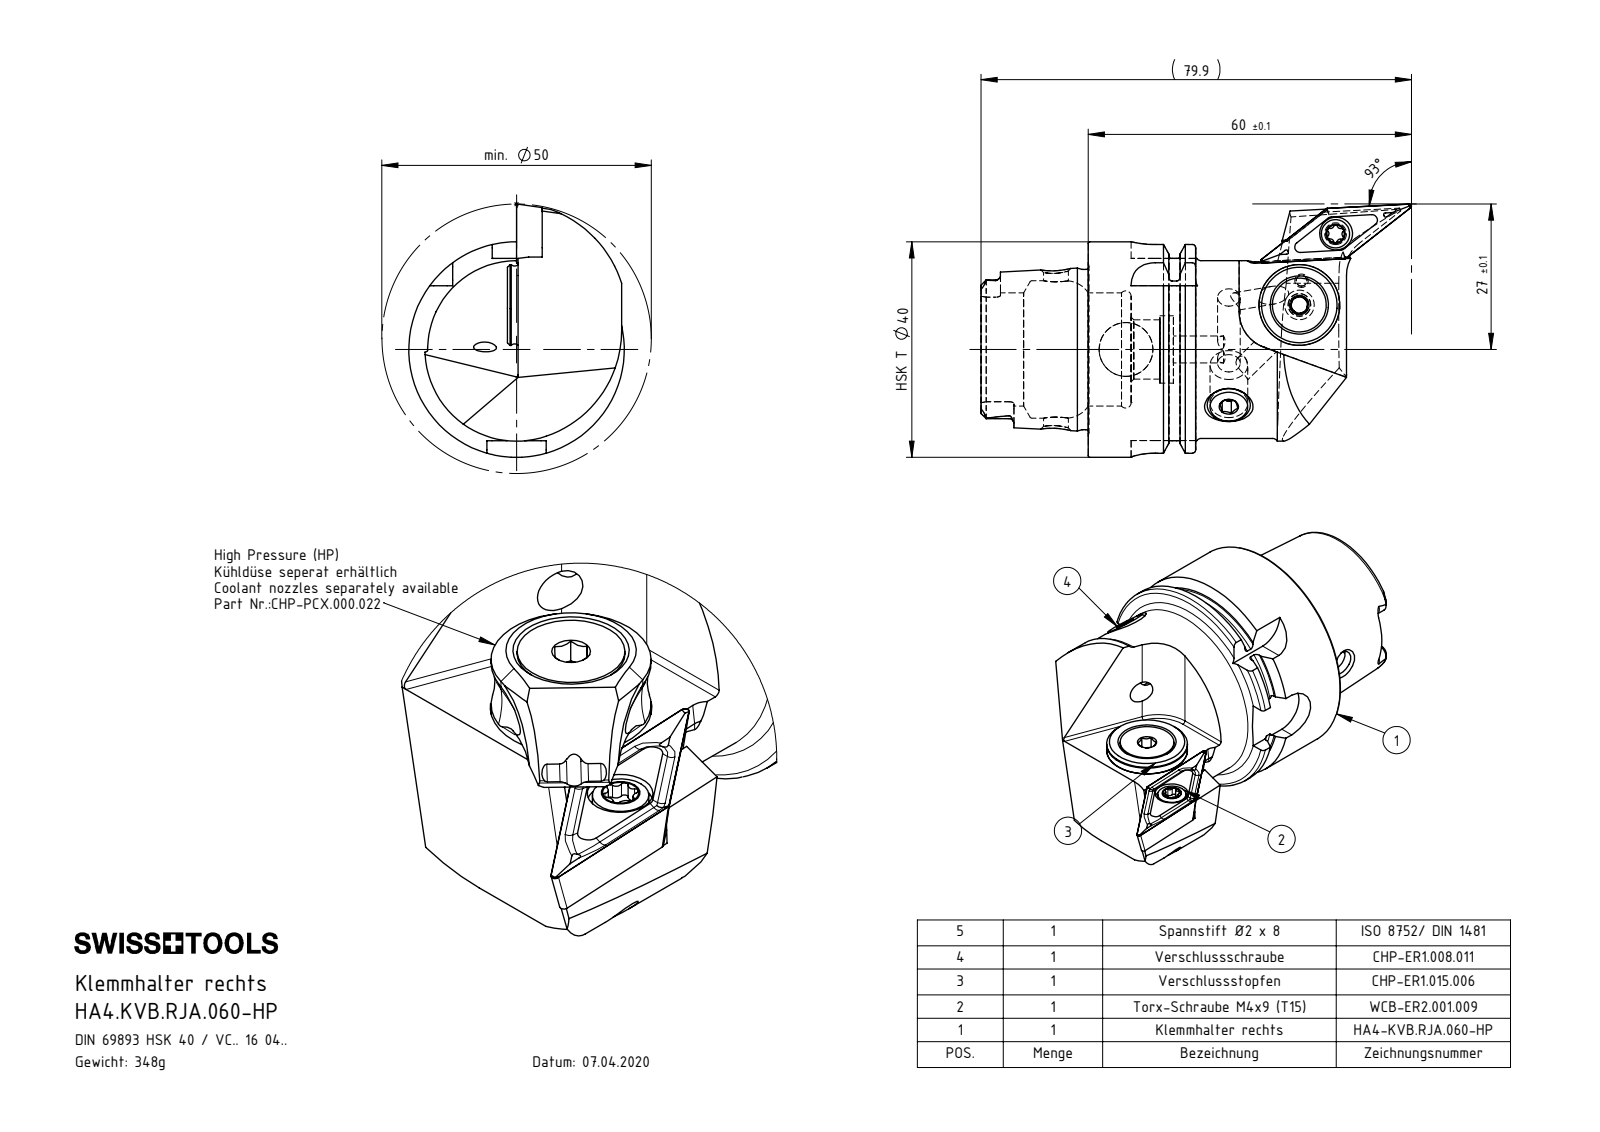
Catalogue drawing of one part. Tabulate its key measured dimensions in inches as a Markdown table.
| quantity | value |
| --- | --- |
| part name | CHP-ER1.015.006; HA4-KVB.RJA.060-HP_A_Fertigbearbeitung; DIN 3771 - 13x1; DIN 7991 - M5x15 (+6 more) |
| STEP written by | SolidWorks 2017 (AUTOMOTIVE_DESIGN) |
| units | inches |
| bodies | 8 solids, 422 faces (122 planar, 120 cylindrical, 180 other) |
| overall size | 3.146 × 1.85 × 1.575 |
| volume | 2.699 in³ |
| surface area | 25.69 in² |
| round holes (diameter × count) | 0.165 × 3, 0.13 × 2, 0.047 × 1, 0.079 × 1, 0.098 × 1, 0.118 × 1, 0.173 × 1, 0.181 × 1, 0.197 × 1, 0.205 × 1, 0.24 × 1, 0.276 × 1 |
| round bosses / shafts (diameter × count) | 1.575 × 1, 1.368 × 1, 1.299 × 1, 1.17 × 1, 0.591 × 1, 0.528 × 1, 0.394 × 1, 0.315 × 1 |
| partial cylindrical surfaces (radius × count) | 0.013 × 6, 0.023 × 6, 0.035 × 6, 0.177 × 4, 0.02 × 2, 0.072 × 2, 0.074 × 2, 0.276 × 2 |
| main face-to-face distances | 0.177, 0.313, 0.472, 0.176, 0.785, 0.579, 0.783, 1.096, 1.569, 0.189 |
| hole center spacings | 0.178, 0.424, 0.428, 0.584, 0.587, 1.308, 1.378, 1.75 |
